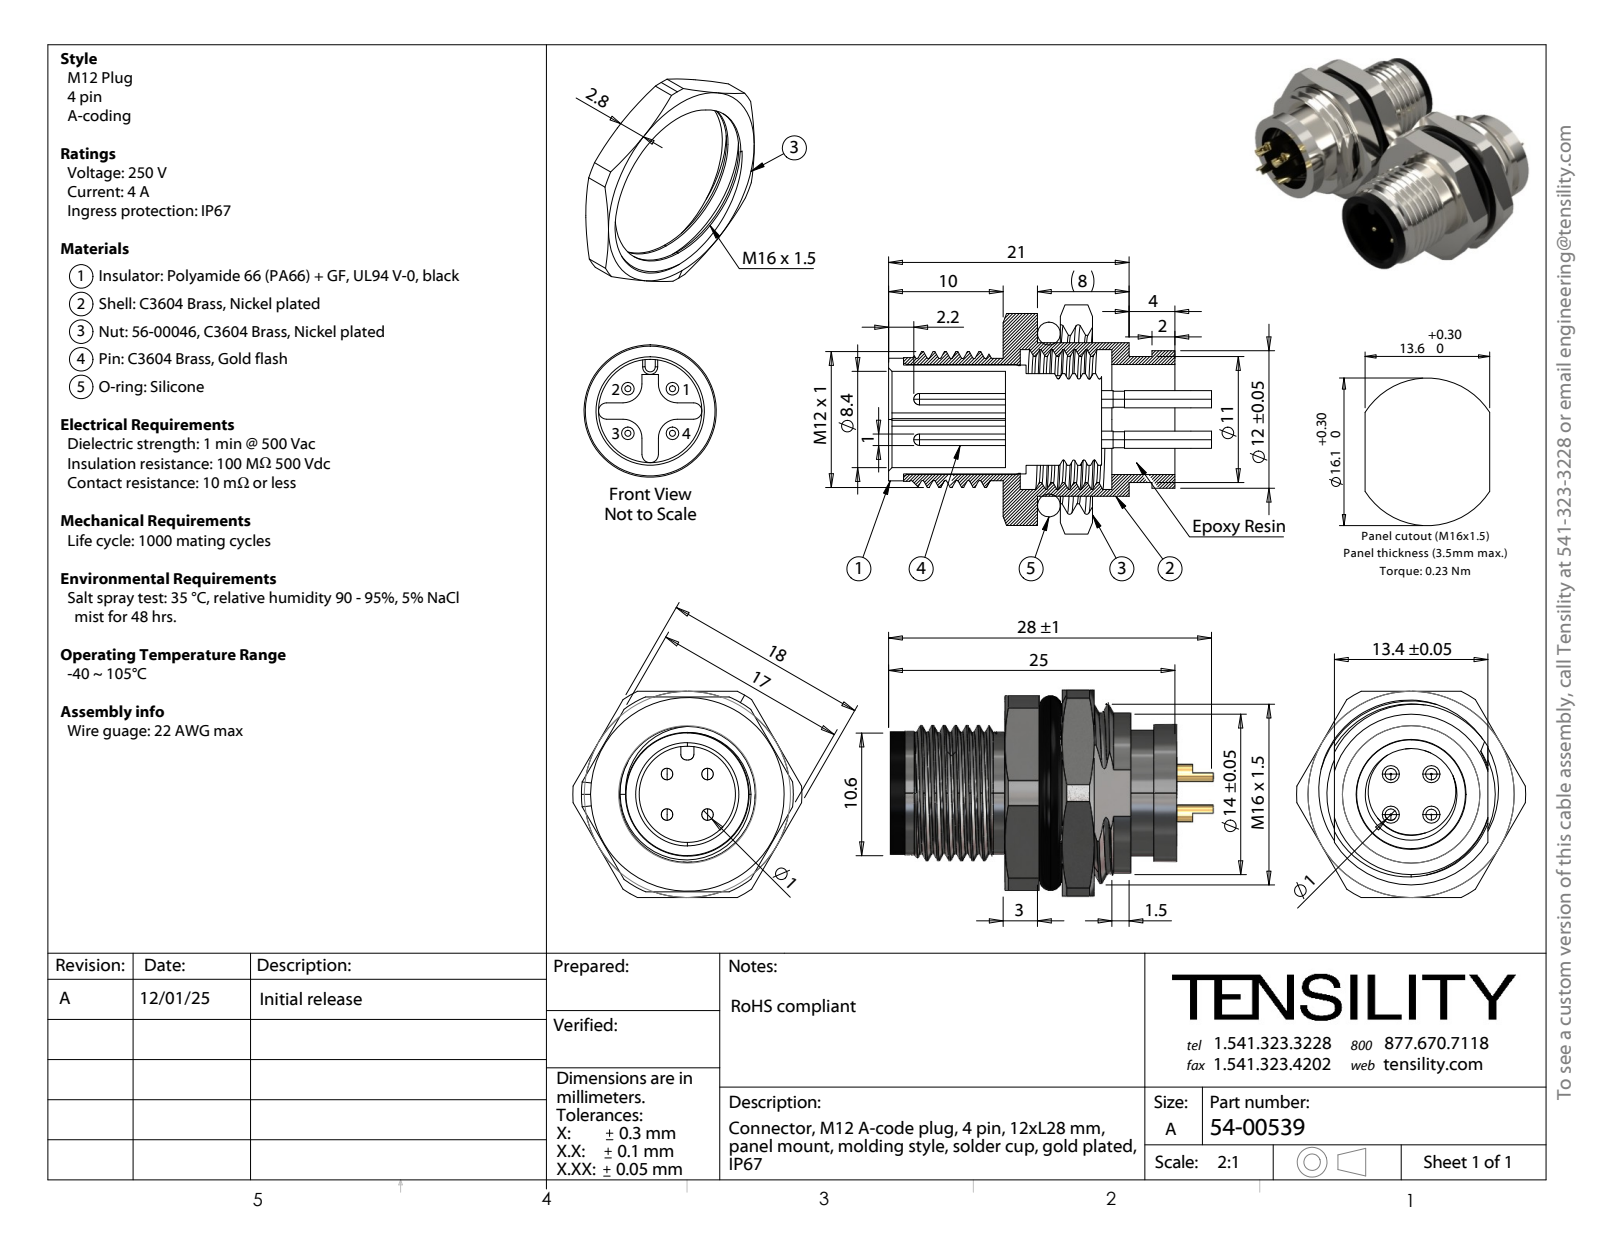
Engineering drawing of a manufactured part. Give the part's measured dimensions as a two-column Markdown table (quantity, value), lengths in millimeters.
| quantity | value |
| --- | --- |
| part name | 54-00539; 56-00046 |
| STEP written by | SolidWorks 2025 (CONFIG_CONTROL_DESIGN) |
| units | millimeters |
| bodies | 4 solids, 301 faces (67 planar, 128 cylindrical, 106 other) |
| overall size | 28.2 × 20 × 18 |
| volume | 2 392 mm³ |
| surface area | 4 820 mm² |
| round holes (diameter × count) | 1 × 3, 0.96 × 1, 8.4 × 1, 9.4 × 1, 9.6 × 1, 12.2 × 1, 14.7 × 1 |
| round bosses / shafts (diameter × count) | 1.5 × 4, 1.4 × 4, 14 × 1, 13.94 × 1, 12 × 1, 11.86 × 1, 11 × 1, 10.8 × 1 |
| partial cylindrical surfaces (radius × count) | 0.5 × 2, 7.9 × 1, 9.25 × 1, 10 × 1 |
| main face-to-face distances | 0.5, 1.5, 17.5, 2, 8, 3, 2.8, 4.8, 9.5, 10 |
| hole center spacings | 2.5, 3.53, 3.54, 5 |
